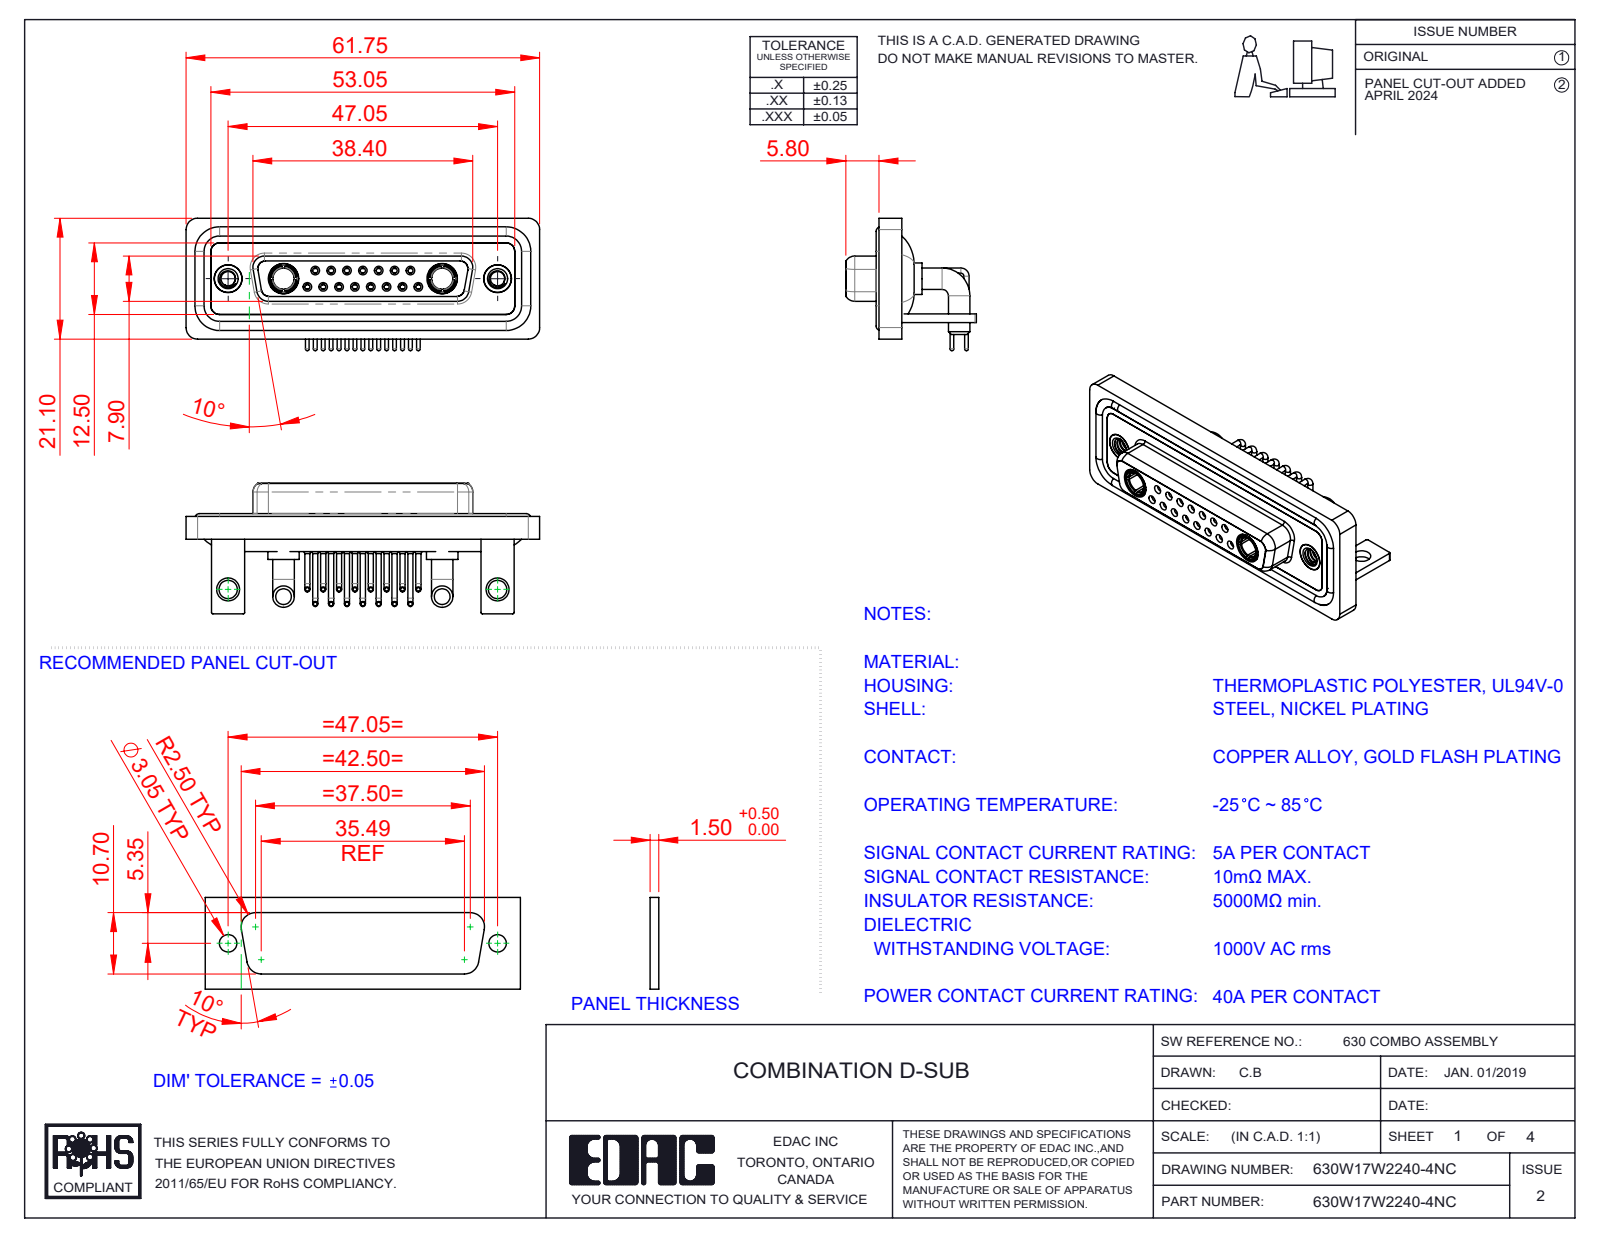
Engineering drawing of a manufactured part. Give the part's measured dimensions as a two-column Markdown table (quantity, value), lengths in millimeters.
| quantity | value |
| --- | --- |
| part name | 630Combo Contact Row 1_50 Contacts; 630Combo Waterproof Housing_25 Contacts; 630Combo Shell Rear_25 Contacts; 630Combo Stabilizer Bracket_50 Contacts (+6 more) |
| STEP written by | SolidWorks 2023 (CONFIG_CONTROL_DESIGN) |
| units | millimeters |
| bodies | 28 solids, 1379 faces (408 planar, 605 cylindrical, 366 other) |
| overall size | 61.75 × 23.12 × 22.8 |
| volume | 8 991 mm³ |
| surface area | 15 356 mm² |
| round holes (diameter × count) | 0.9 × 15, 1.1 × 15, 1.5 × 15, 2 × 15, 1.6 × 8, 1.7 × 7, 4.85 × 4, 2.5 × 2, 3.2 × 2, 3.7 × 2, 4 × 2, 4.05 × 2 |
| round bosses / shafts (diameter × count) | 0.9 × 15, 0.65 × 15, 1.6 × 11, 3.75 × 4, 5.5 × 2, 5.2 × 2, 4.96 × 2, 4.95 × 2 |
| partial cylindrical surfaces (radius × count) | 2 × 19, 1.5 × 18, 0.25 × 16, 1.35 × 8, 1.6 × 8, 0.5 × 5, 0.6 × 4, 0.65 × 4 |
| main face-to-face distances | 0.4, 1.8, 2.9, 3.7, 1.5, 4.1, 1.1, 1.4, 1.6, 3.1 |
| hole center spacings | 3.16, 2.77, 5.54, 8.31, 5.04, 7.49, 11.08, 5.03 |
